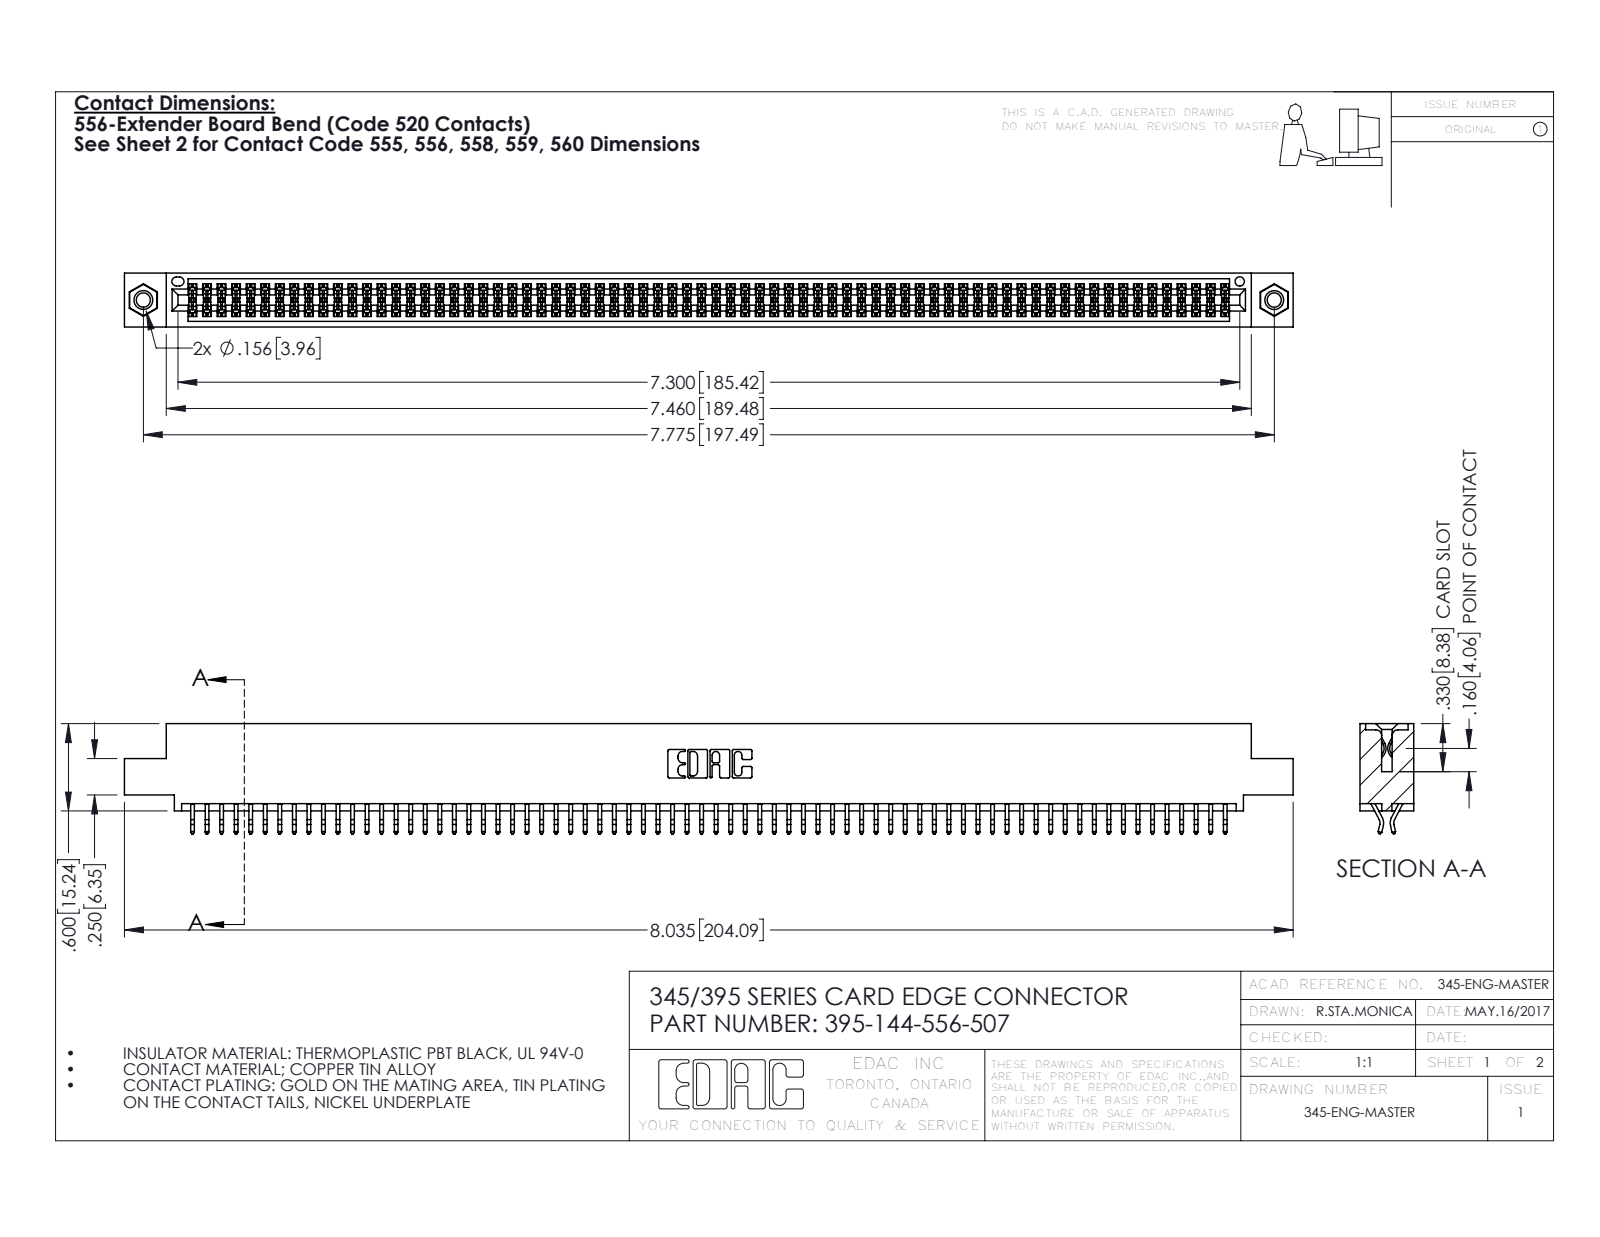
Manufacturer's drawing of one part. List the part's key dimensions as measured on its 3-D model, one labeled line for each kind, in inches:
Part name (STEP PRODUCT): 395-144-556-507; 345-250-001_345-250-005-103; 345 Part_0.110 Offset - 0.156 Dia-TI; 345-292-001_556 Tail
STEP written by: SolidWorks 2016 (CONFIG_CONTROL_DESIGN)
Units: inches
Bodies: 147 solids, 8254 faces (5444 planar, 2794 cylindrical, 16 other)
Overall size (bounding box): 8.035 × 0.757 × 0.37
Volume: 1.221 in³ · Surface area: 46.74 in²
Round holes (diameter × count): ⌀0.098 ×2, ⌀0.125 ×2, ⌀0.156 ×2, ⌀0.064 ×1
Round bosses / shafts (diameter × count): ⌀0.155 ×2
Partial cylindrical surfaces — rounded edges, fillets, slot ends (radius × count): R0.006 ×216, R0.01 ×22, R0.007 ×6, R0.031 ×6, R0.026 ×3, R0.01 ×2, R0.014 ×2, R0.019 ×2
Main face-to-face distances: 0.072, 0.298, 0.37, 0.2, 0.025, 0.098, 0.272, 0.225, 0.175, 0.149
Hole centre spacings: 0.27, 7.539, 7.775
